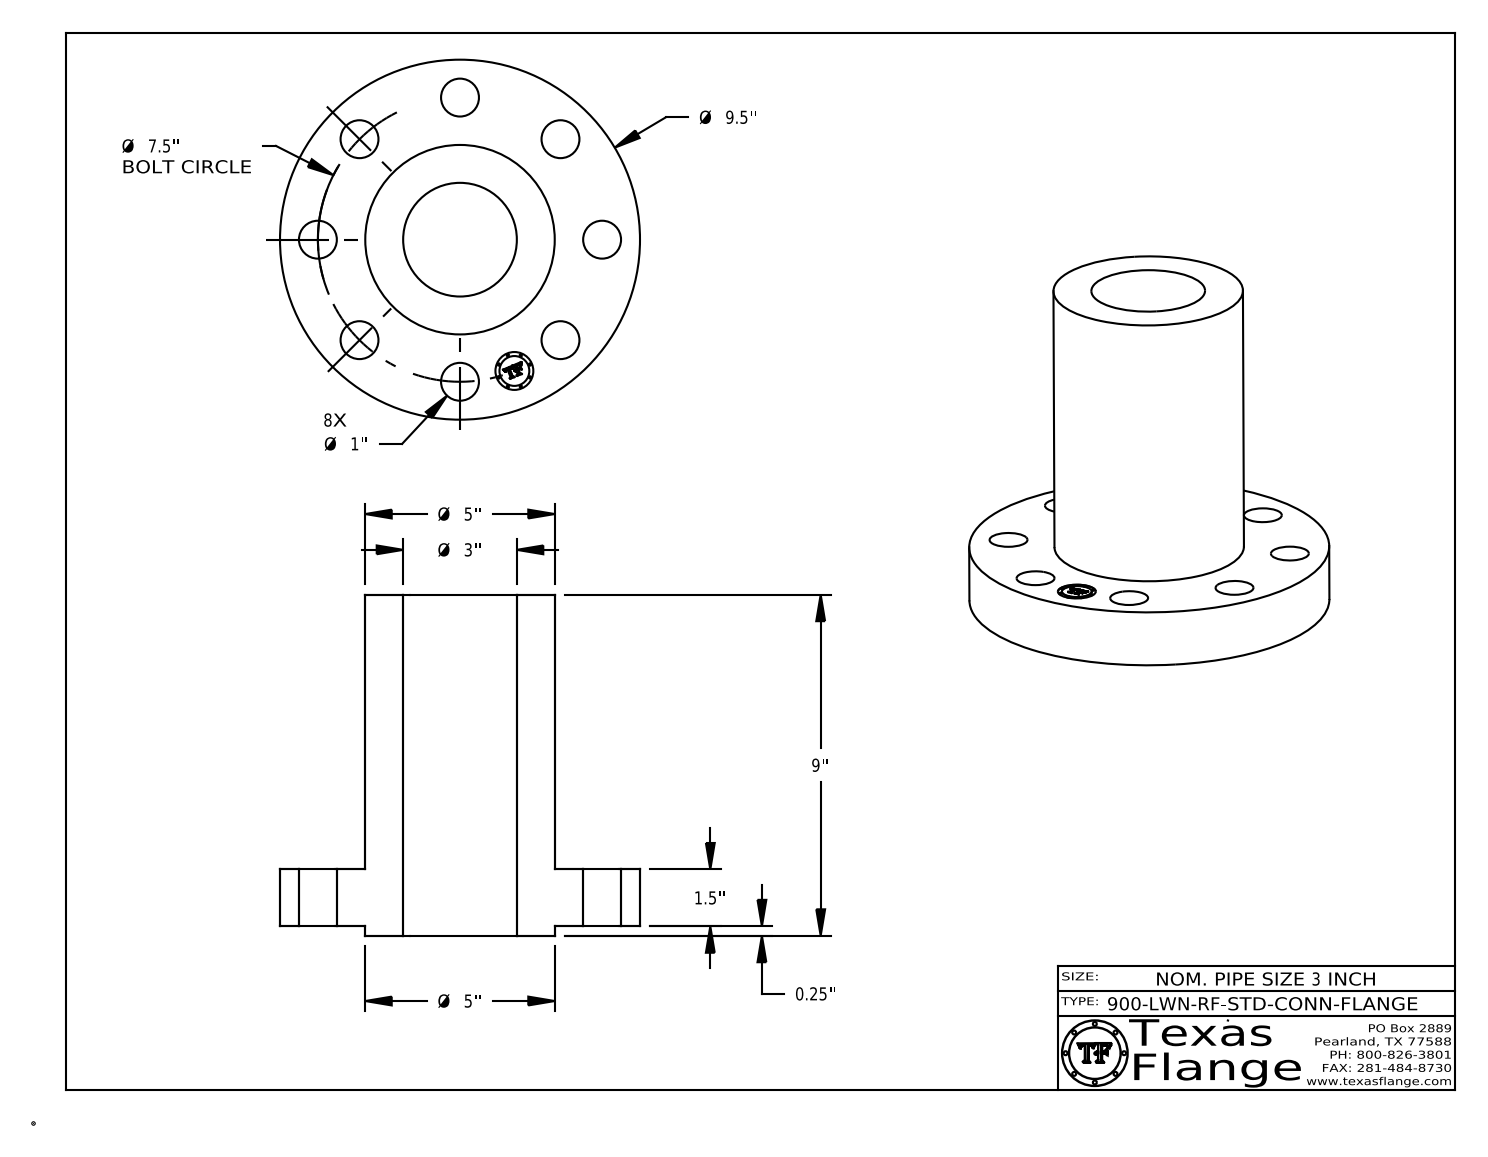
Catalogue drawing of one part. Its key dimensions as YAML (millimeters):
part_name: "3-900-LWN-RF-STD-CONN-FLANGE"
step_written_by: "CATIA V5 STEP AP214 (AUTOMOTIVE_DESIGN)"
units: millimeters
bodies: {solids: 1, faces: 413, planar: 369, cylindrical: 44, other: 0}
overall_size: [241.3, 241.3, 228.6]
volume: 2958000
surface_area: 258200
round_holes:
  - {diameter: 25.4, count: 9}
  - {diameter: 76.2, count: 1}
round_bosses_or_shafts:
  - {diameter: 1.5, count: 8}
  - {diameter: 241.3, count: 1}
  - {diameter: 127, count: 1}
  - {diameter: 20, count: 1}
face_to_face_distances: [38.1, 6.4, 44.5, 228.6, 222.3, 184.2, 44.3, 38, 184.3, 7.6]
hole_center_spacings: [95.3, 72.9, 134.7, 176, 37.2, 158.4, 186.8, 190.5]
